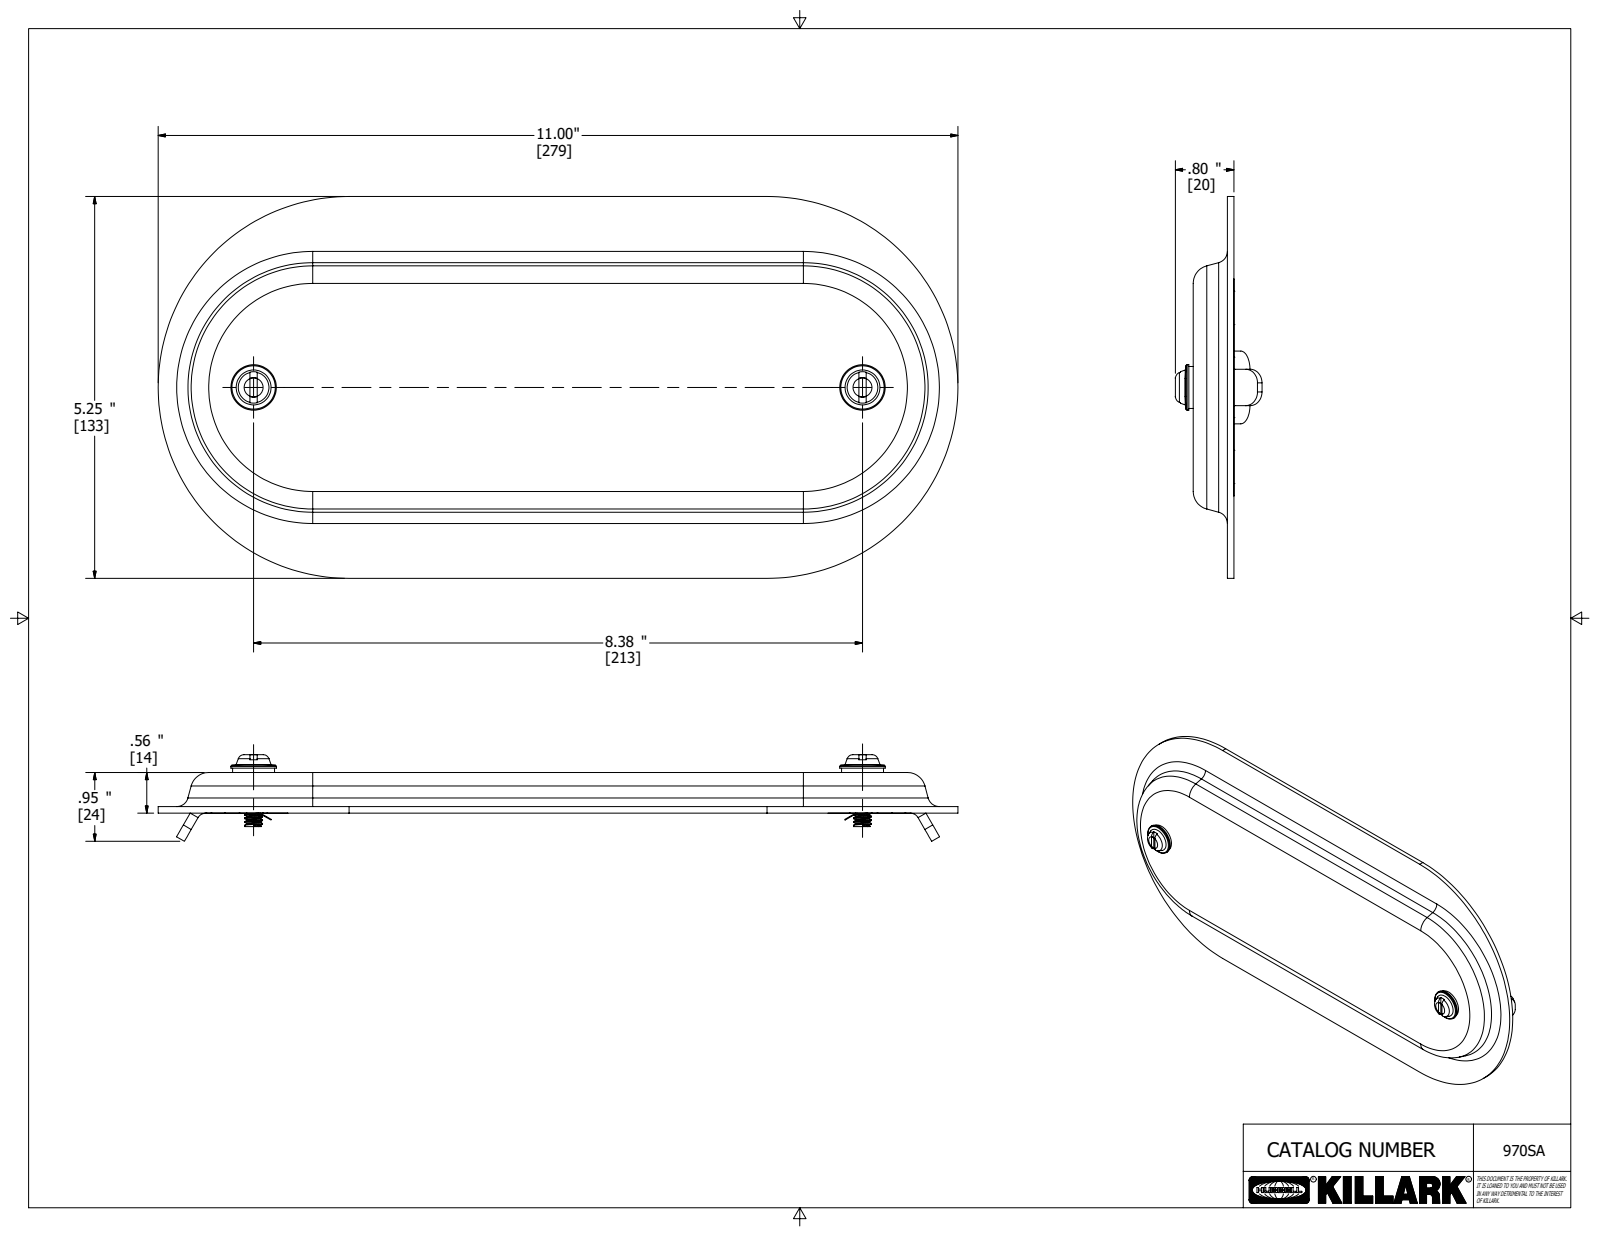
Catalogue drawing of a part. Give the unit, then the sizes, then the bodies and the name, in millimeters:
Units: millimetres
Overall size (bounding box): 279.4 × 133.4 × 30.3
Round holes (diameter × count): ⌀6.4 ×2, ⌀8.7 ×2
Round bosses / shafts (diameter × count): ⌀15.9 ×2, ⌀14.7 ×2, ⌀6.2 ×2, ⌀5 ×2
Partial cylindrical surfaces — rounded edges, fillets, slot ends (radius × count): R4.7 ×8, R6.4 ×8, R3.2 ×4, R4.1 ×4, R12.7 ×4, R22.2 ×4, R5.6 ×2, R66.7 ×2
Main face-to-face distances: 2.3, 11.9, 14.2, 2.3, 9.6, 11.9, 3.2, 0.9, 8.7, 11
Hole centre spacings: 212.7
Volume: 103 800 mm³ · Surface area: 90 770 mm²
Bodies: 5 solids, 156 faces (76 planar, 52 cylindrical, 28 other)
Part name (STEP PRODUCT): 970SA; 17747; 18038CABB; 17953
STEP written by: Autodesk Inventor 2018 (AUTOMOTIVE_DESIGN)
